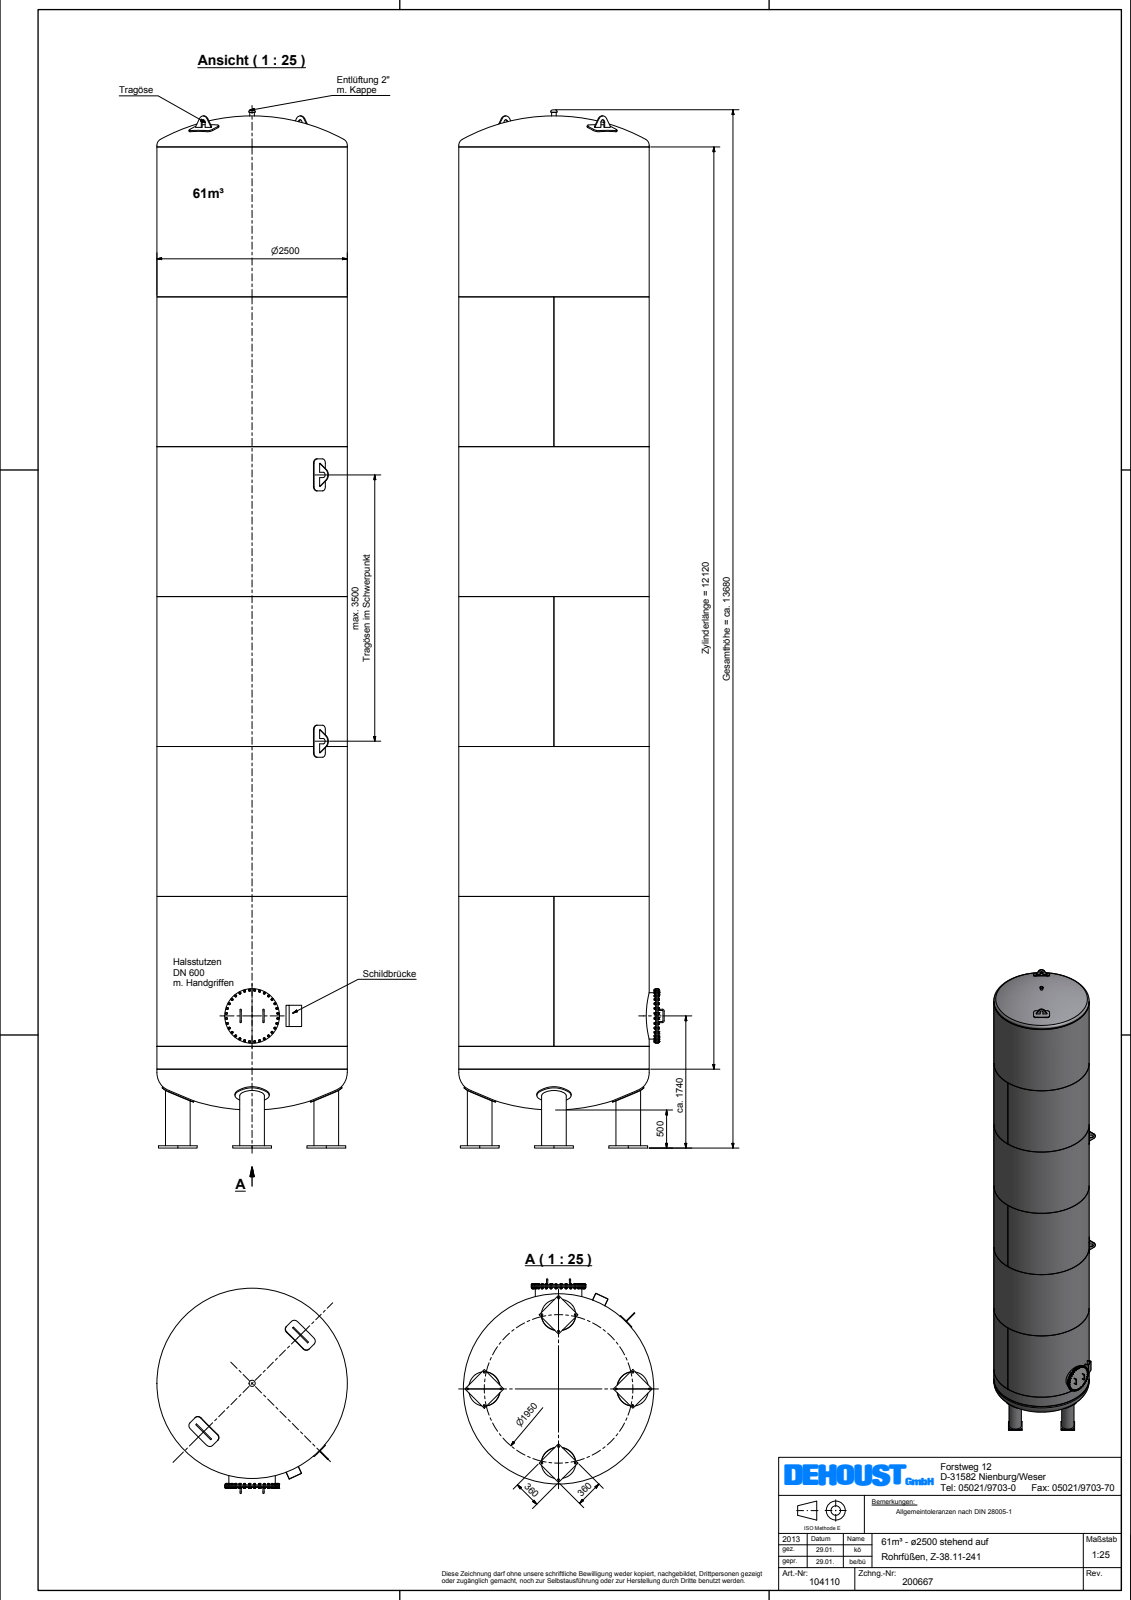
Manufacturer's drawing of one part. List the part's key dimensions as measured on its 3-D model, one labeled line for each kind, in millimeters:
Part name (STEP PRODUCT): Beh\S\dlter_Z-38_11-241_2500_061_KV
STEP written by: Autodesk Inventor 2012 (AUTOMOTIVE_DESIGN)
Units: millimetres
Bodies: 6 solids, 228 faces (133 planar, 65 cylindrical, 30 other)
Overall size (bounding box): 13563.78 × 2619 × 2500
Volume: 2 568 000 000 mm³ · Surface area: 221 700 000 mm²
Round holes (diameter × count): ⌀200 ×4, ⌀306.9 ×4, ⌀60.3 ×1, ⌀598 ×1, ⌀2480 ×1, ⌀2486 ×1, ⌀2488 ×1
Round bosses / shafts (diameter × count): ⌀450 ×4, ⌀323.9 ×4, ⌀2500 ×1, ⌀720 ×1, ⌀610 ×1
Partial cylindrical surfaces — rounded edges, fillets, slot ends (radius × count): R56 ×16, R35 ×4, R85 ×4, R1260 ×1
Main face-to-face distances: 1036.54, 30, 1006.54, 16, 359.95, 1378.65, 2.95, 176.98, 2.91, 10
Hole centre spacings: 975, 1378.86, 1950
